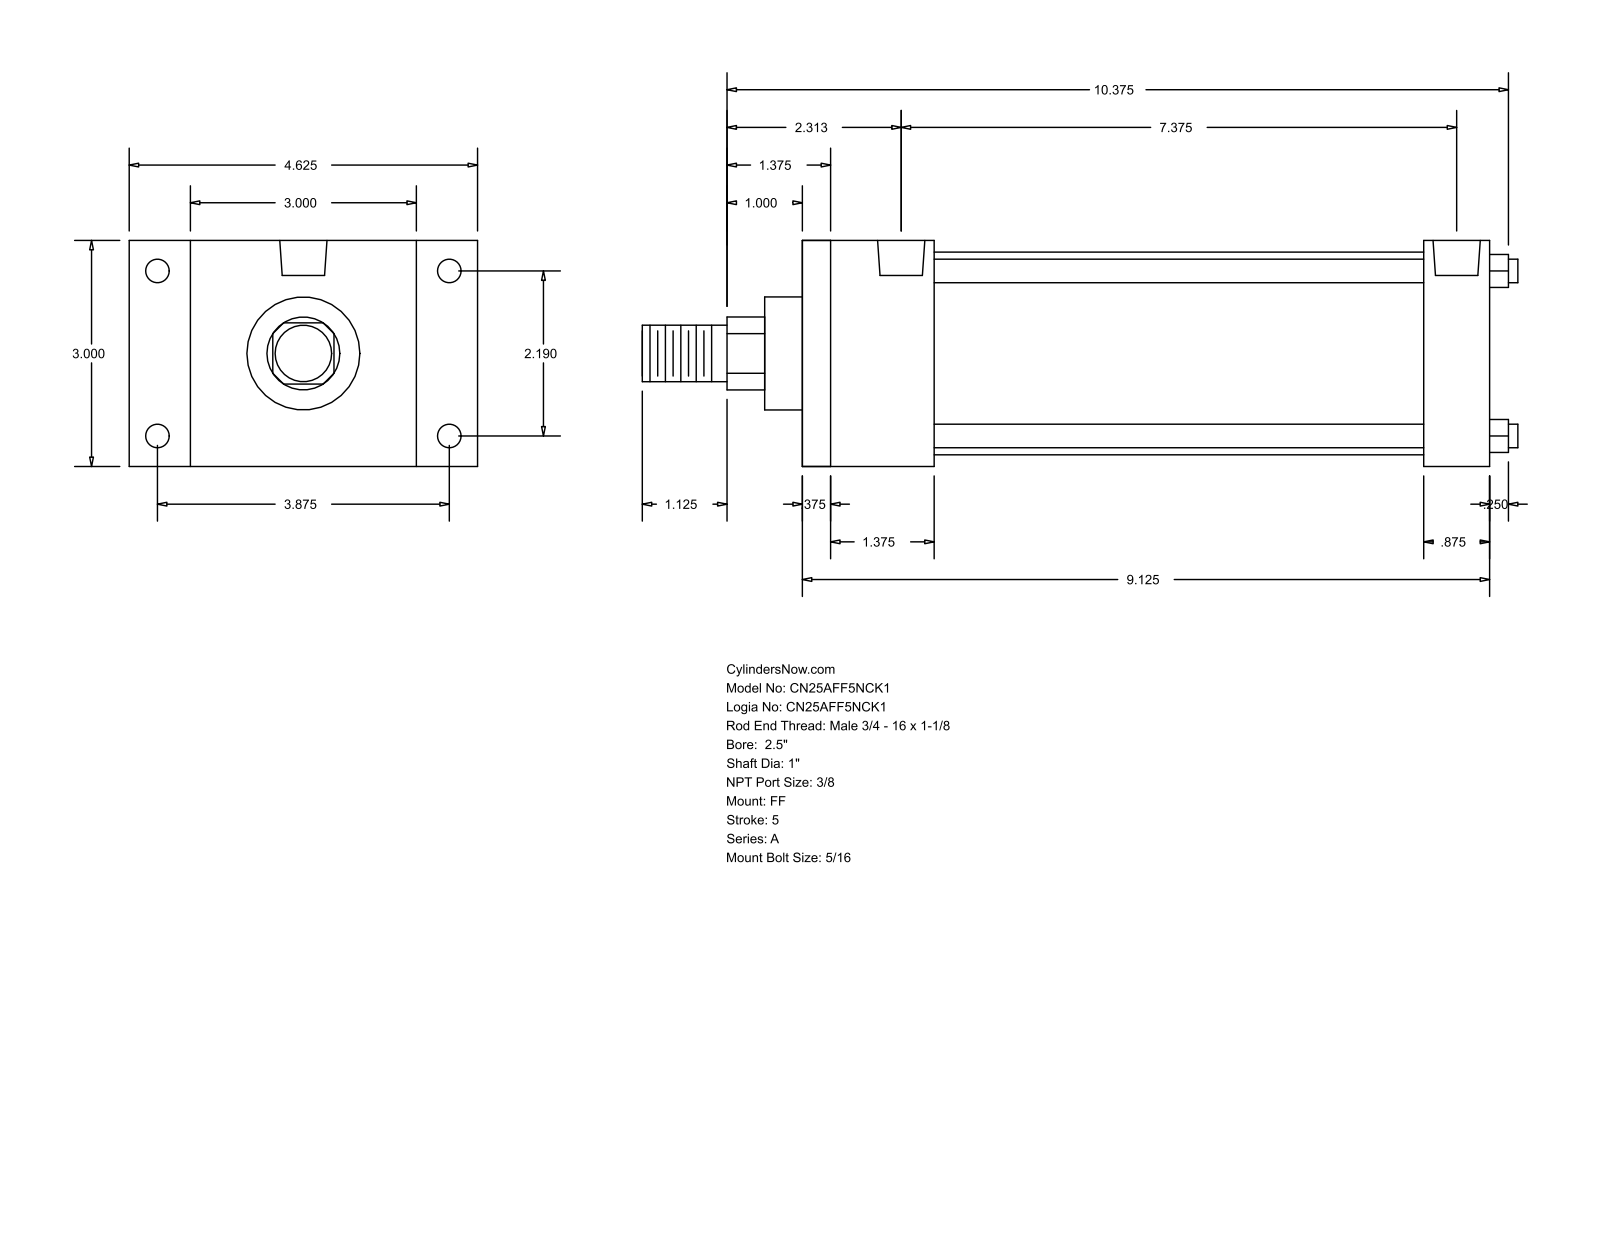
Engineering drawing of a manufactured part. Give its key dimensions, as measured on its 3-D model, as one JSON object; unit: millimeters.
{"part_name": "A_FF__0250_1", "step_written_by": "GSSL Pune (CONFIG_CONTROL_DESIGN)", "units": "millimeters", "bodies": {"solids": 0, "faces": 92, "planar": 64, "cylindrical": 28, "other": 0}, "overall_size": [295.27, 117.47, 76.2], "round_holes": [[5.56, 4], [7.94, 4], [15.93, 2]], "round_bosses_or_shafts": [[7.94, 4], [68.33, 1], [38.1, 1], [25.4, 1], [19.05, 1]], "partial_cylinders_radius": [[12.29, 1]], "face_to_face_distances": [76.2, 231.78, 9.52, 222.26, 44.45, 209.55, 34.93, 200.03, 165.1, 187.33], "hole_center_spacings": [2.38, 55.62, 98.42, 113.05, 189.7, 192.08, 187.32]}
